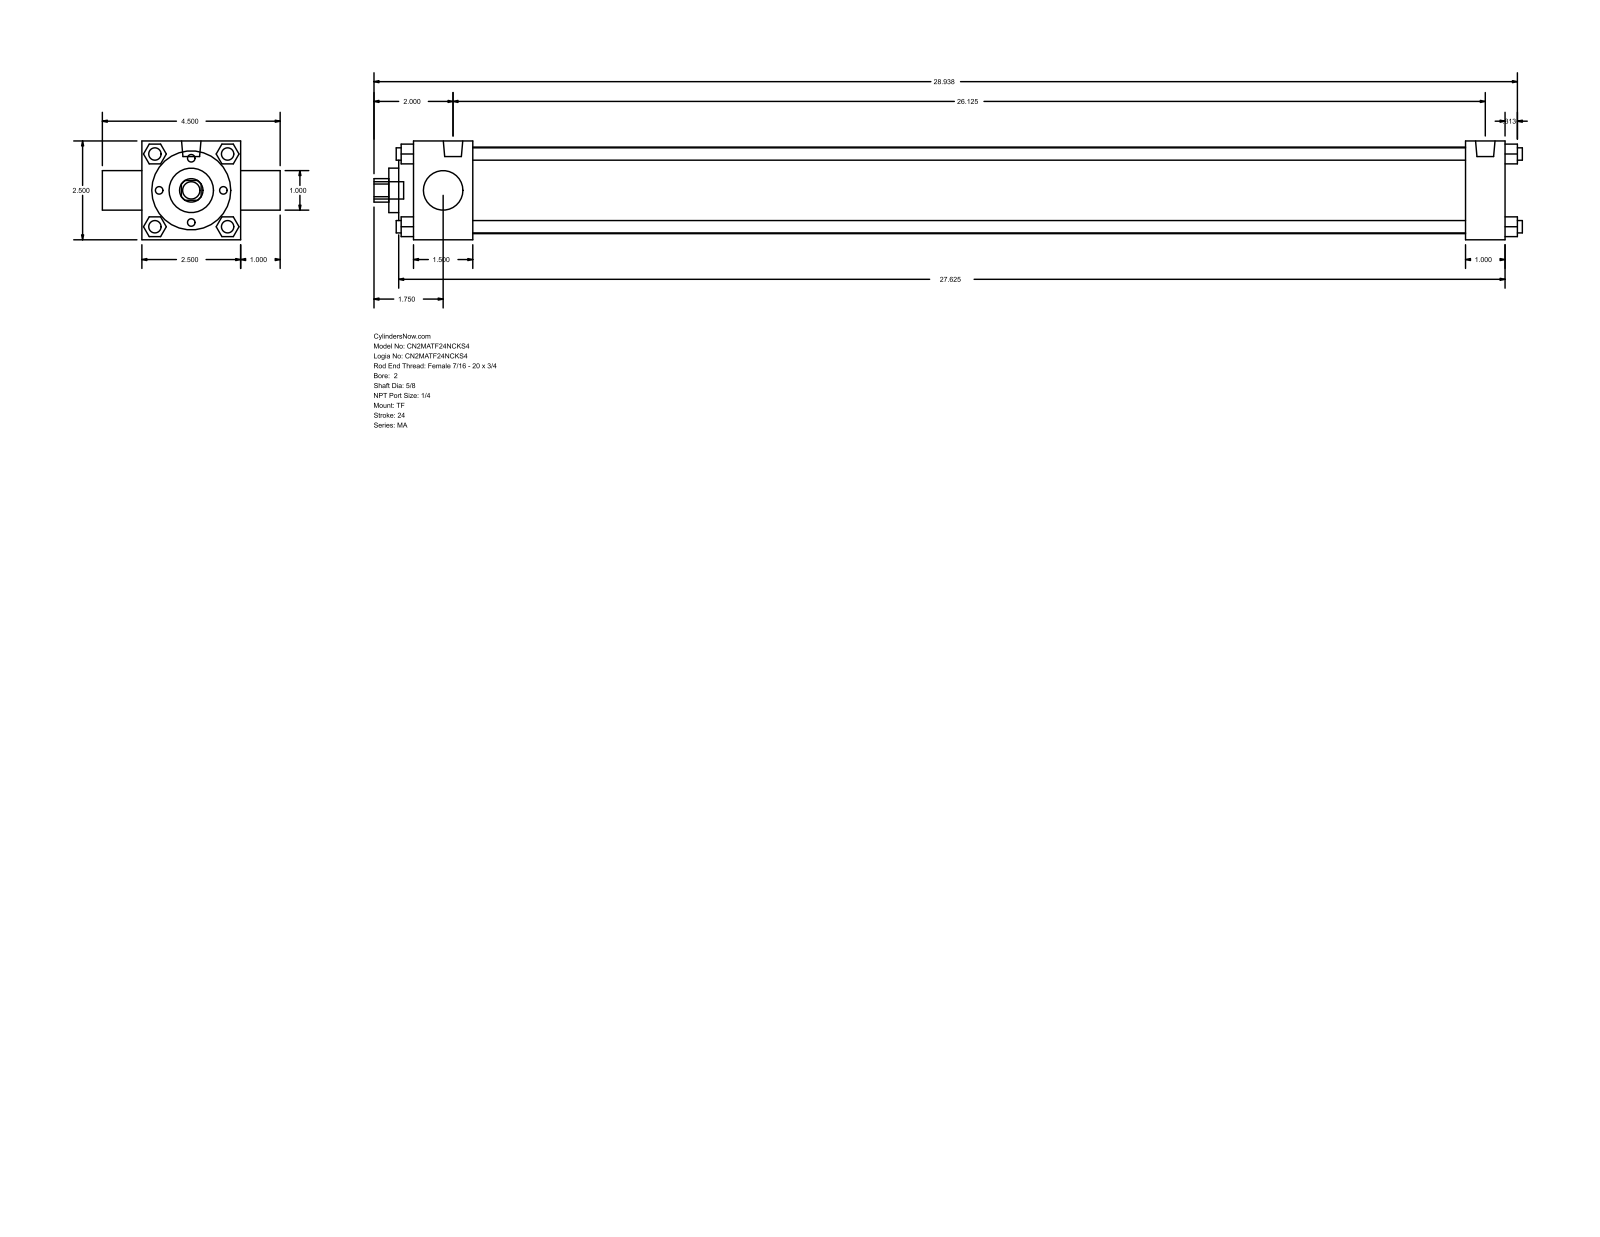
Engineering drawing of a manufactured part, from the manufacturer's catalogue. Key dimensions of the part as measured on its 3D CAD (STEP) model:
Part name (STEP PRODUCT): MA_TF__0200_0.625
STEP written by: GSSL Pune (CONFIG_CONTROL_DESIGN)
Units: millimetres
Bodies: 0 solids, 122 faces (93 planar, 29 cylindrical, 0 other)
Overall size (bounding box): 738.19 × 114.3 × 63.5
Round holes (diameter × count): ⌀15.88 ×1, ⌀25.4 ×1, ⌀28.57 ×1, ⌀50.8 ×1, ⌀55.63 ×1
Round bosses / shafts (diameter × count): ⌀7.94 ×7, ⌀12.49 ×2, ⌀11.11 ×1
Partial cylindrical surfaces — rounded edges, fillets, slot ends (radius × count): R7.54 ×1
Main face-to-face distances: 63.5, 38.1, 12.7, 9.52, 701.68, 676.27, 638.17, 663.58, 25.41, 47.62
